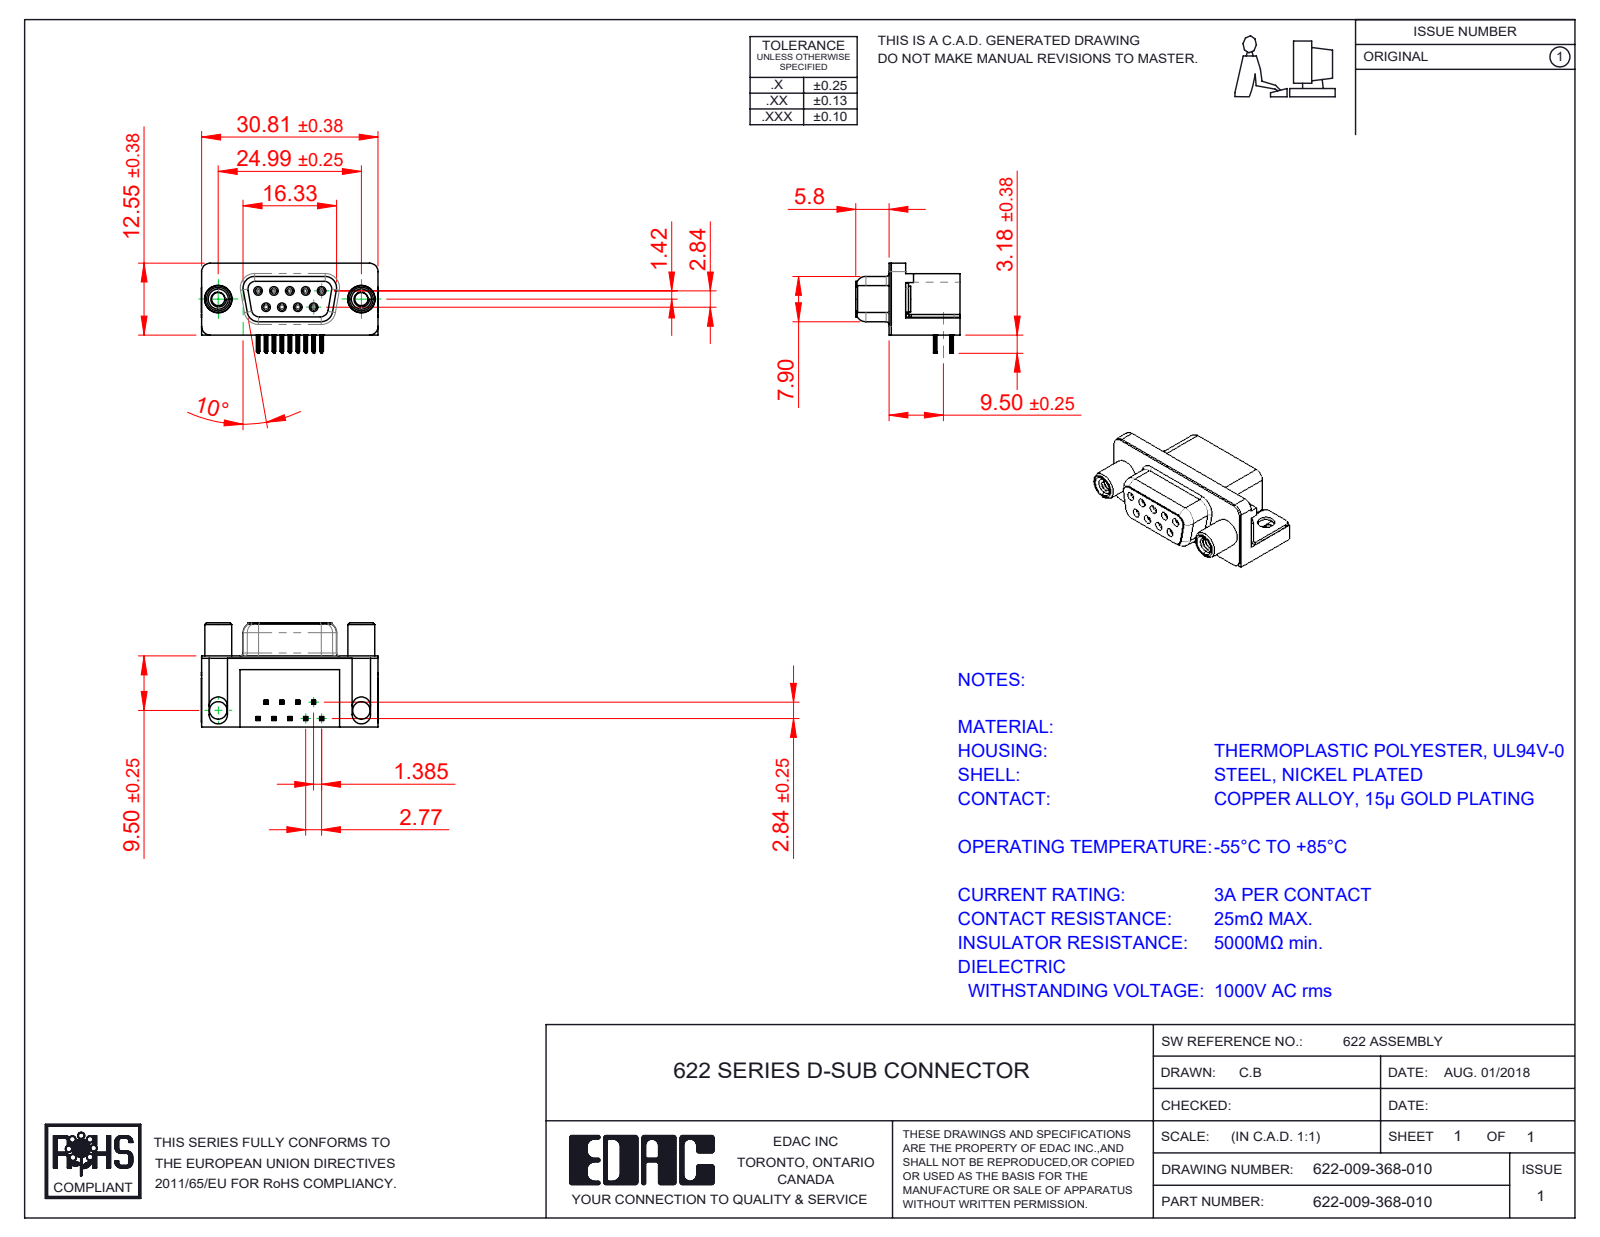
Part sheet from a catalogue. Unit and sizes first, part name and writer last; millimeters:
Units: millimetres
Overall size (bounding box): 30.89 × 18.2 × 15.73
Round holes (diameter × count): ⌀0.8 ×9, ⌀0.9 ×9, ⌀2.3 ×2, ⌀3.05 ×2, ⌀3.1 ×2, ⌀4 ×2, ⌀4.8 ×2, ⌀5 ×2
Round bosses / shafts (diameter × count): ⌀1.2 ×9, ⌀4.9 ×2, ⌀4.7 ×2, ⌀4.5 ×2, ⌀3.85 ×2
Partial cylindrical surfaces — rounded edges, fillets, slot ends (radius × count): R0.1 ×72, R0.15 ×36, R0.35 ×18, R1 ×18, R0.34 ×9, R1.35 ×8, R1.6 ×8, R1.5 ×7
Main face-to-face distances: 0.4, 12, 12.4, 0.35, 2.9, 2.5, 10.34, 5.8, 9.5, 6.2
Hole centre spacings: 3.16, 2.77, 5.54, 5.03, 5.04, 8.31, 7.48, 7.49
Volume: 3 814 mm³ · Surface area: 5 260 mm²
Bodies: 15 solids, 1564 faces (674 planar, 424 cylindrical, 466 other)
Part name (STEP PRODUCT): 622 Socket Bottom; 622 Contact Top; 622-009-368-010; 622 Shell_9 Socket (+3 more)
STEP written by: SolidWorks 2016 (CONFIG_CONTROL_DESIGN)
